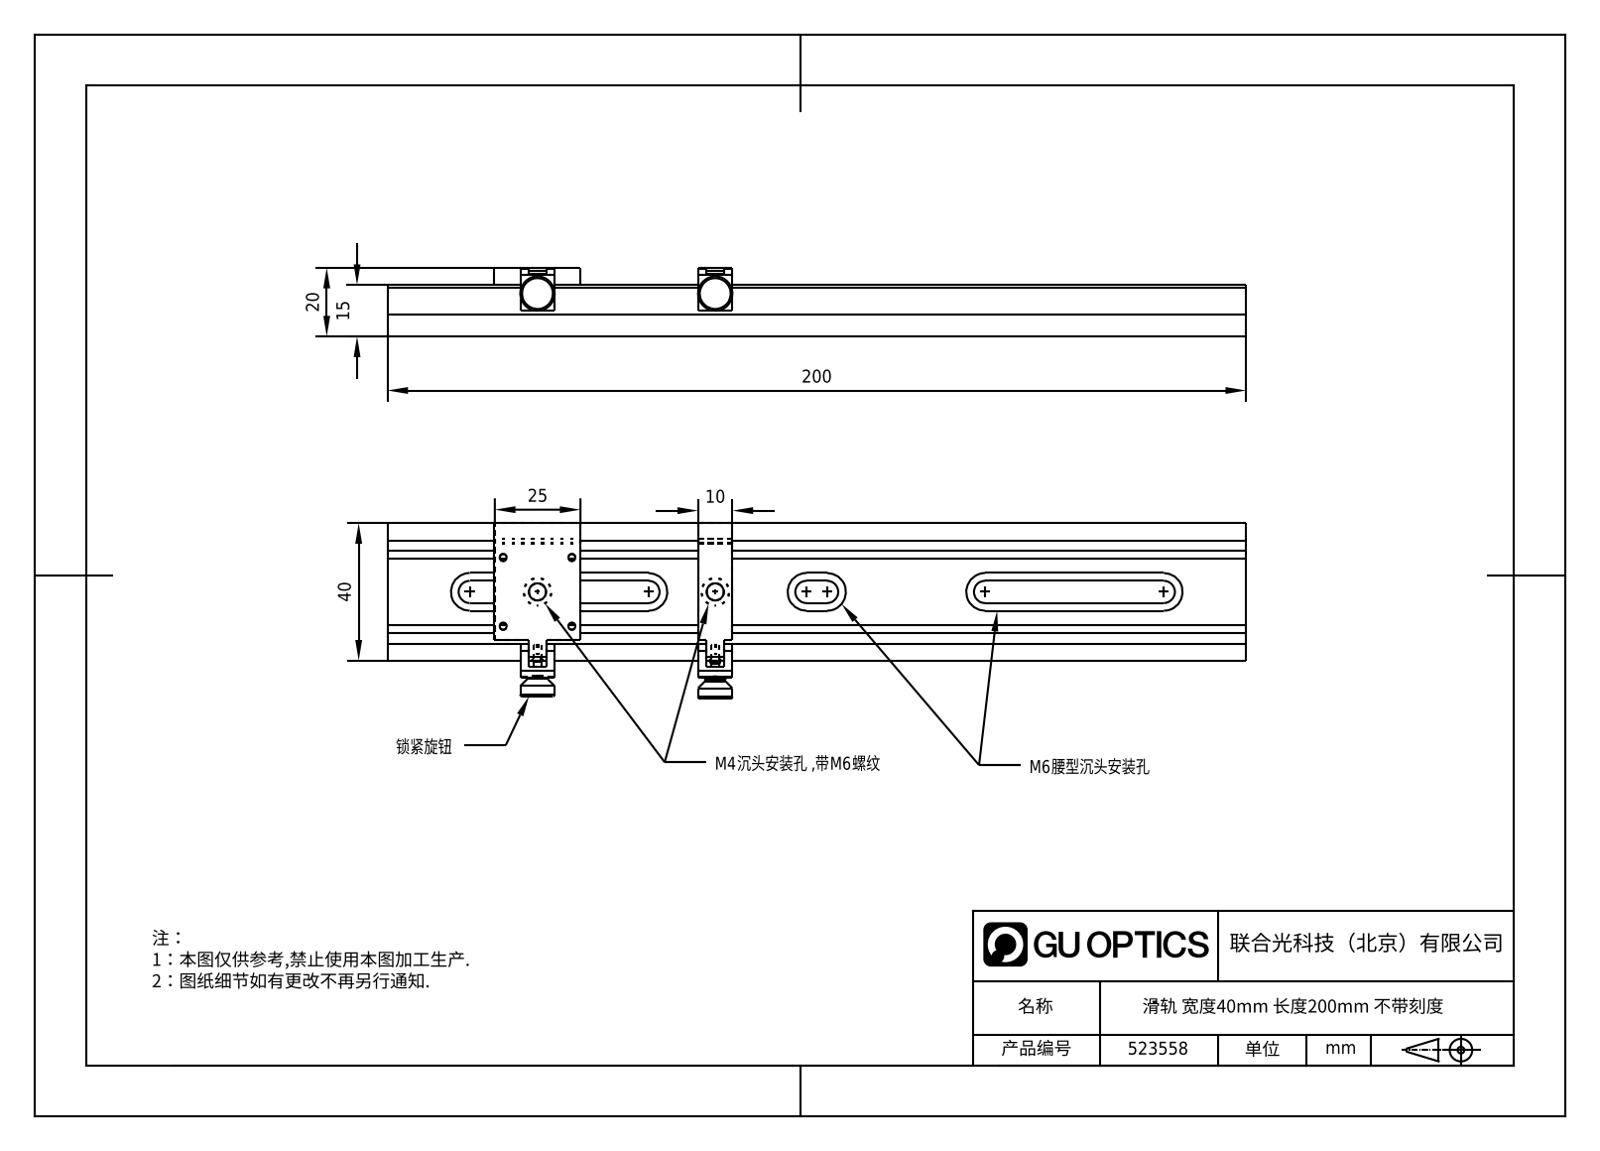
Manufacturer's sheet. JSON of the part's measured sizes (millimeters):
{"part_name": "4.2.2.2，H40Z-25，40mm滑轨安装座，宽度25mm，A; 4.2.2.1，H40Z-10，40mm滑轨安装座，宽度10mm，A; 4.2.1.8.1，40mm滑轨主体，长度200mm; 4.2.2.1.2，40mm滑轨安装座压块，宽度25mm，B (+5 more)", "step_written_by": "SolidWorks 2021 (CONFIG_CONTROL_DESIGN)", "units": "millimeters", "bodies": {"solids": 8, "faces": 221, "planar": 110, "cylindrical": 83, "other": 28}, "overall_size": [200, 52.09, 20], "volume_mm3": 78111, "surface_area_mm2": 34024, "round_holes": [[2.05, 4], [2.5, 2], [3.2, 2], [5, 2], [8, 2], [1.5, 1], [2, 1]], "round_bosses_or_shafts": [[10, 2], [6, 2], [3, 2], [2.2, 2]], "partial_cylinders_radius": [[3.25, 6], [5.5, 6], [1.25, 1], [2.5, 1], [4.5, 1], [12.5, 1]], "face_to_face_distances": [14.5, 6, 0.5, 15, 5, 6.5, 8.5, 8, 40, 19.5], "hole_center_spacings": [14.14, 20, 28.28, 52.66, 61.7, 72.39]}
